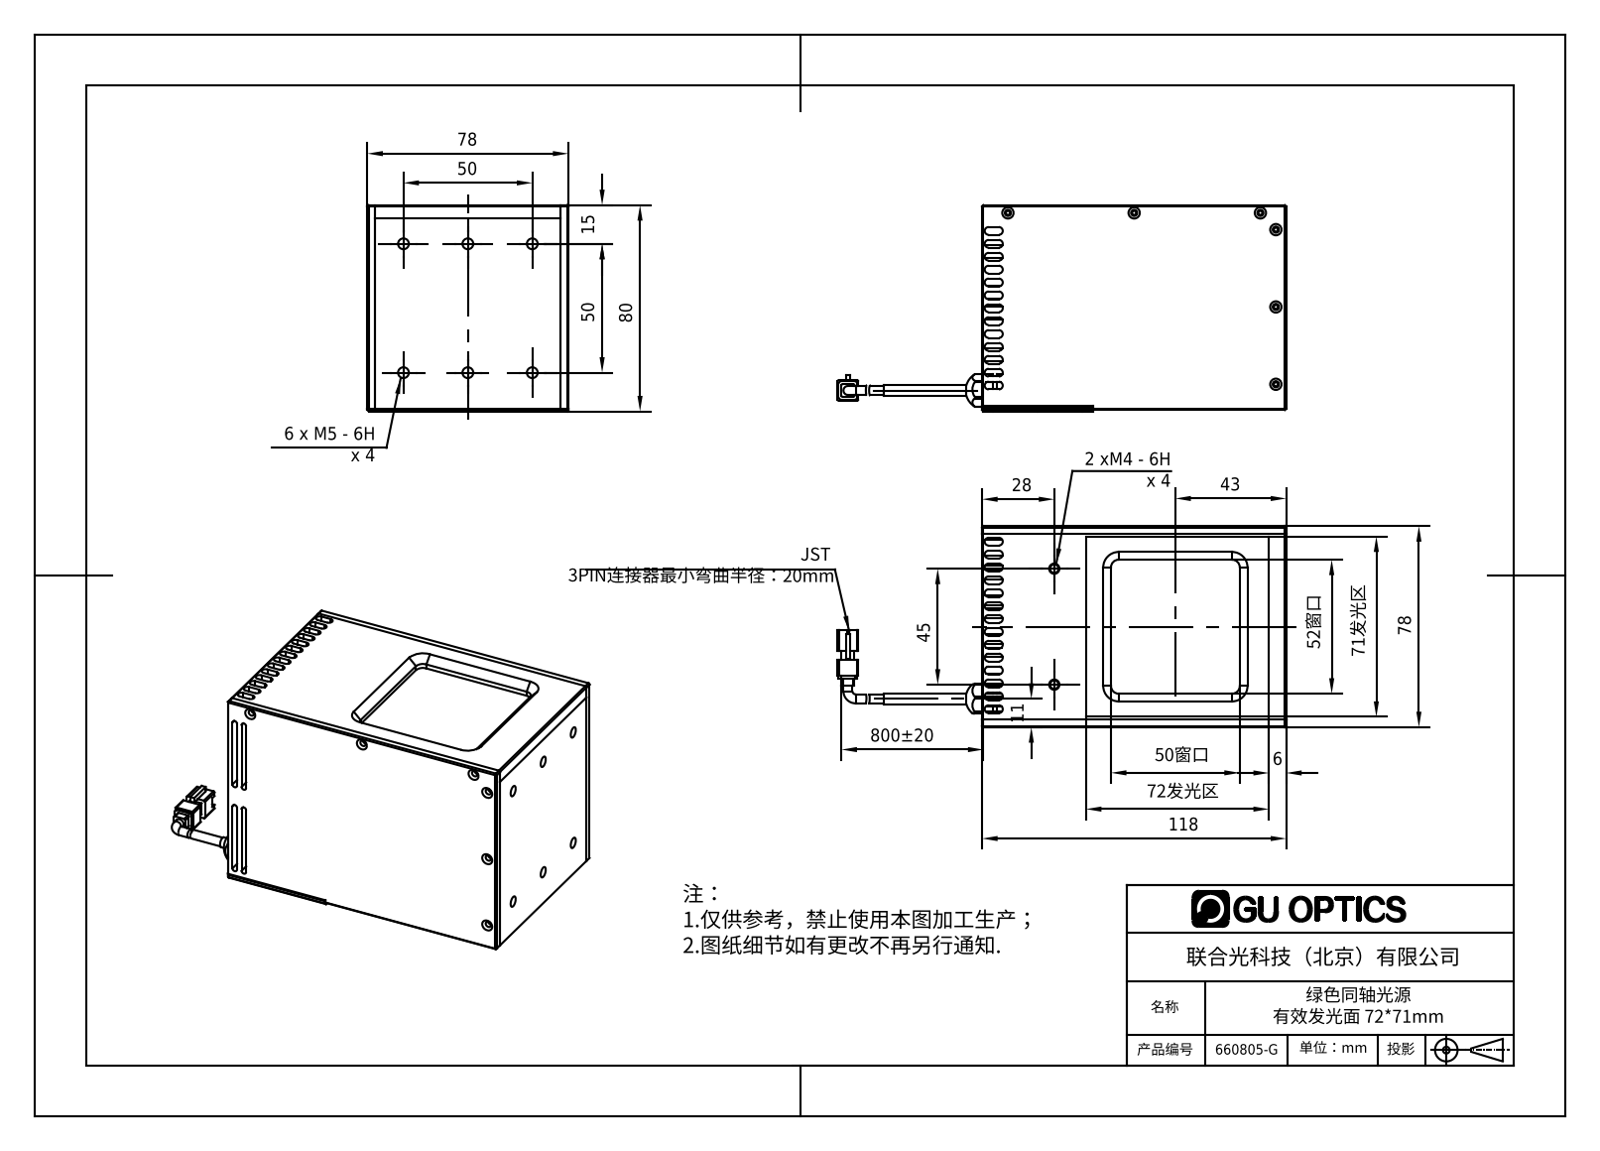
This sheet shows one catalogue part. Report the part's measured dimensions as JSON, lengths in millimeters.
{"part_name": "绿色同轴光源 有效发光面 7271mm", "step_written_by": "SolidWorks 2016 (AUTOMOTIVE_DESIGN)", "units": "millimeters", "bodies": {"solids": 23, "faces": 1600, "planar": 1165, "cylindrical": 278, "other": 157}, "overall_size": [151.44, 80.2, 78], "volume_mm3": 196586, "surface_area_mm2": 164600, "round_holes": [[2.4, 16], [1.6, 15], [2, 9], [4.2, 6], [7, 4], [3.8, 1], [6.8, 1], [9, 1]], "round_bosses_or_shafts": [[3.5, 2], [9.76, 1], [8, 1], [4, 1]], "partial_cylinders_radius": [[1.5, 54], [1, 12], [0.5, 8], [2, 4], [3, 4], [0.8, 1], [6.25, 1]], "face_to_face_distances": [1, 4, 74, 6, 75, 78, 100, 3, 2, 70], "hole_center_spacings": [50, 17.5, 25, 55.9, 75.07, 70, 73, 1.1]}
